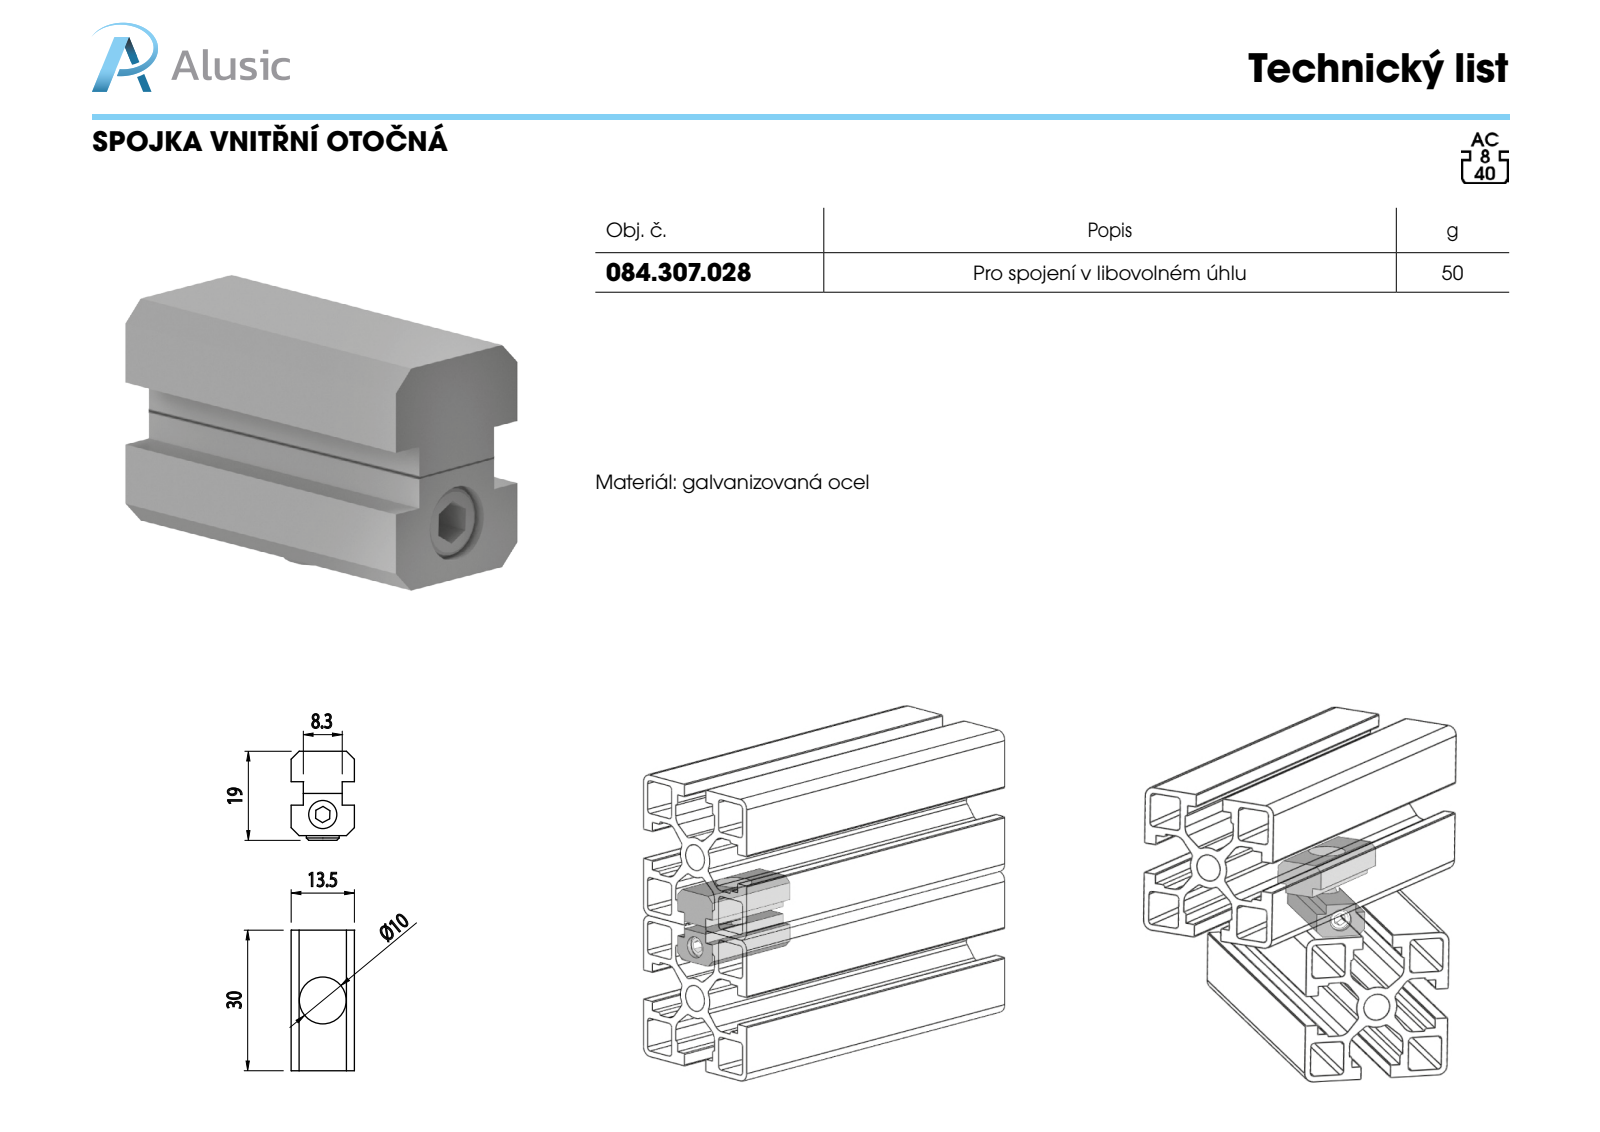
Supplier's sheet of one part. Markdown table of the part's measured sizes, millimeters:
| quantity | value |
| --- | --- |
| part name | 084.307.028; Socket Set Screw Cup Point_ALUSIC_ISO 4029 - M6 x 12-S; 084.307.028B; 084.307.028C (+1 more) |
| STEP written by | SolidWorks 2011 (CONFIG_CONTROL_DESIGN) |
| units | millimeters |
| bodies | 4 solids, 129 faces (35 planar, 34 cylindrical, 60 other) |
| overall size | 30 × 19 × 13.5 |
| volume | 6 283 mm³ |
| surface area | 4 407 mm² |
| round holes (diameter × count) | 7 × 1, 10 × 1 |
| round bosses / shafts (diameter × count) | 6 × 1 |
| main face-to-face distances | 9, 6.5, 2.5, 11.5, 2.6, 10.9, 13.5, 18, 30, 5 |
